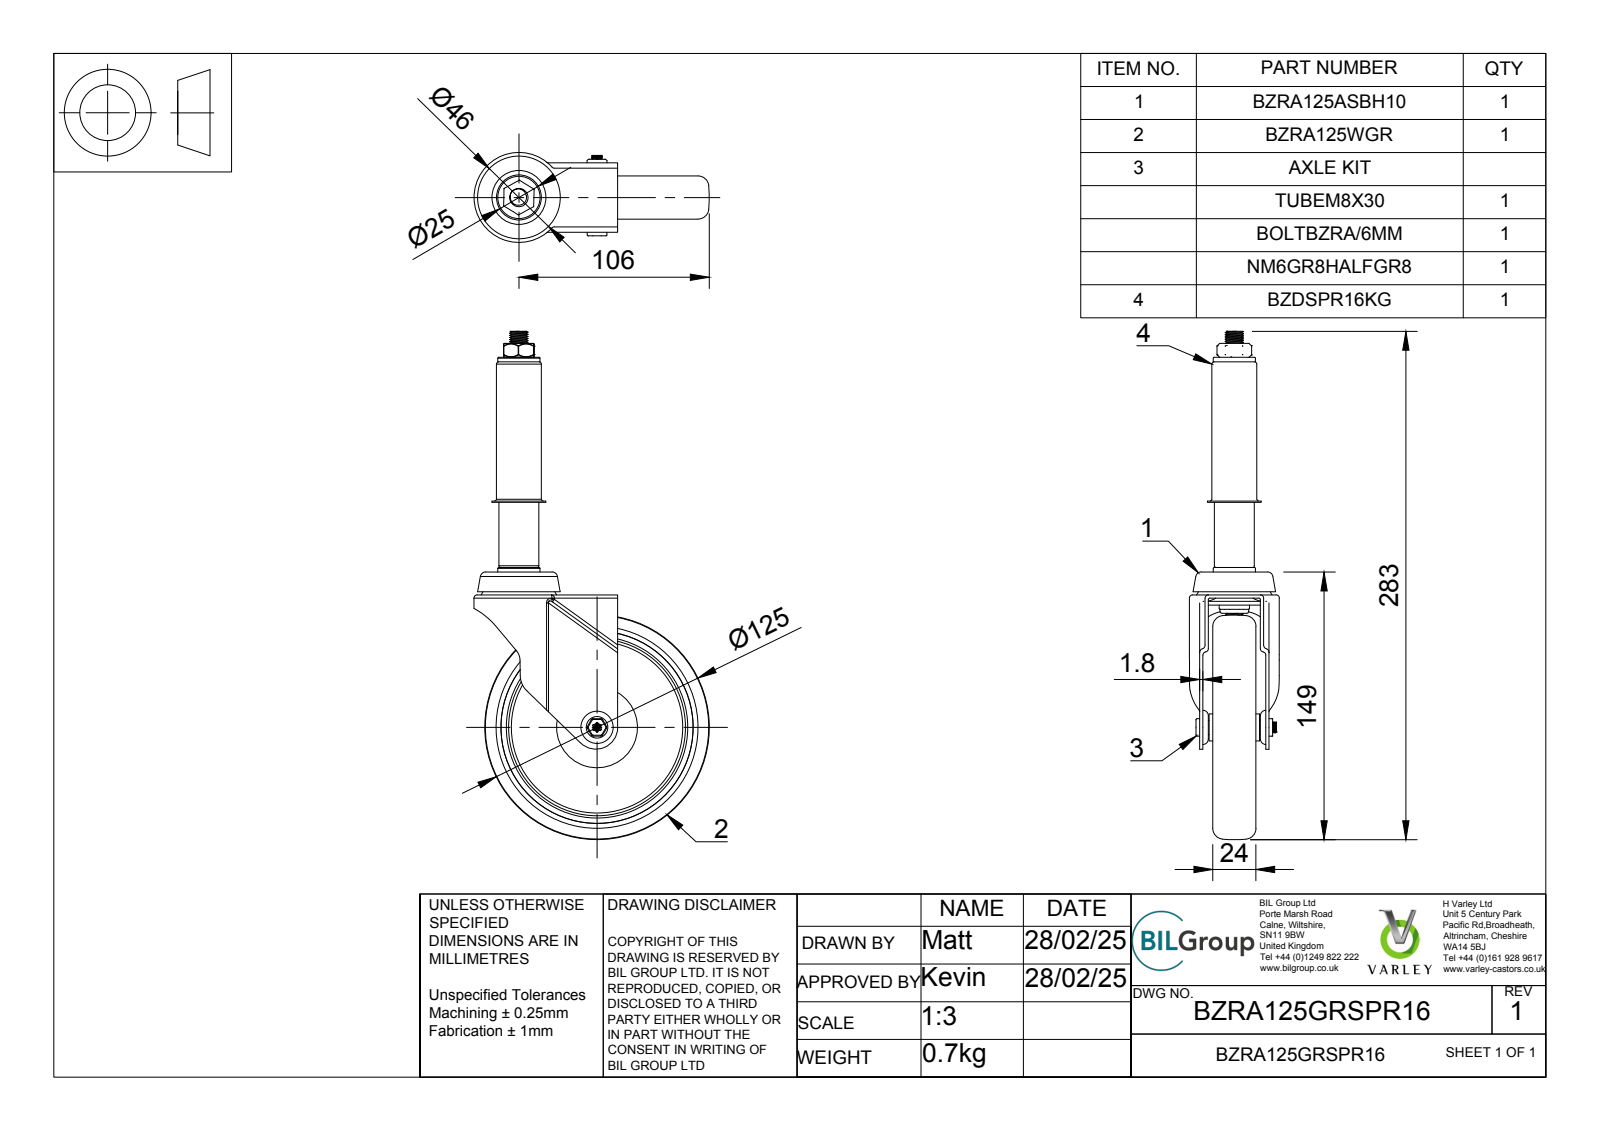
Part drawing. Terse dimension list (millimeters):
name: BZRA125GRSPR16 v3; BZRA125ASBH10 v1; ZINC PLATED PRESSED STEEL FORKS; ZINC PLATED PRESSED STEEL HEAD (+8 more)
written by: Autodesk Translation Framework v13.20.0.188 (AP242_MANAGED_MODEL_BASED_3D_ENGINEERING_MIM_LF)
unit: mm
bodies: 17 solids, 458 faces (116 planar, 178 cylindrical, 164 other)
size: 283.43 × 131 × 50
volume: 229 811 mm³; area: 134 857 mm²
holes: 1× ⌀6, 1× ⌀6.3, 1× ⌀6.4, 1× ⌀8.2, 1× ⌀8.3, 1× ⌀10, 1× ⌀10.5, 1× ⌀10.56, 1× ⌀12, 1× ⌀13, 1× ⌀15, 1× ⌀16.5
bosses: 1× ⌀39, 1× ⌀30, 1× ⌀25, 1× ⌀23.5, 1× ⌀22.25, 1× ⌀19.8, 1× ⌀18, 1× ⌀16
rounds: 30× R0.5, 18× R1, 14× R1.8, 6× R0.25, 6× R0.4, 6× R0.9, 1× R2.12, 1× R8
face distances: 5.5, 14.75, 1.8, 16.55, 22.05, 7.3, 31.3, 9.25, 33.8, 3
